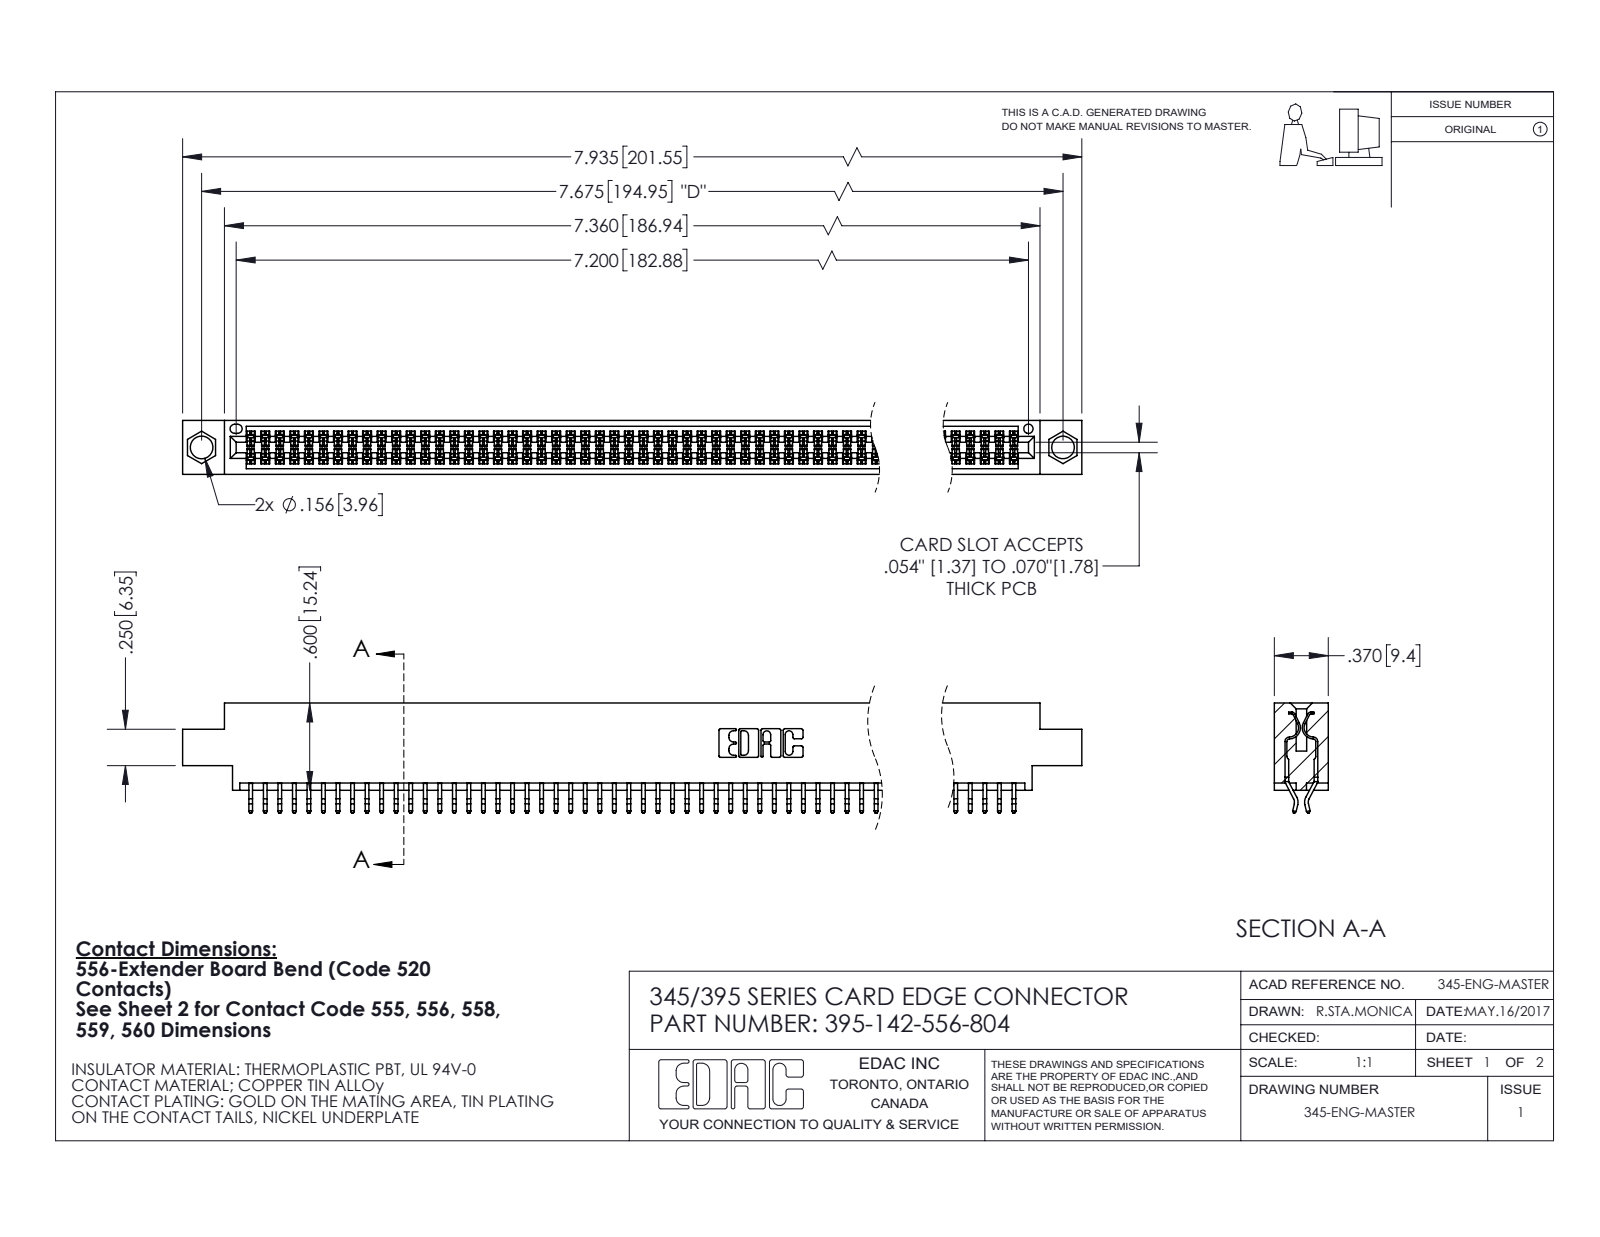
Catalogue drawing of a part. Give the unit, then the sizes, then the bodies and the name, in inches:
Units: inches
Overall size (bounding box): 7.935 × 0.757 × 0.37
Round holes (diameter × count): ⌀0.156 ×2, ⌀0.064 ×1
Partial cylindrical surfaces — rounded edges, fillets, slot ends (radius × count): R0.006 ×284, R0.01 ×22, R0.007 ×6, R0.031 ×6, R0.026 ×3, R0.01 ×2, R0.014 ×2, R0.019 ×2
Main face-to-face distances: 0.072, 0.298, 0.37, 0.2, 0.025, 0.098, 0.272, 0.225, 0.175, 0.149
Hole centre spacings: 0.27, 7.439, 7.675
Volume: 1.197 in³ · Surface area: 45.63 in²
Bodies: 143 solids, 8096 faces (5352 planar, 2744 cylindrical, 0 other)
Part name (STEP PRODUCT): 395-142-556-804; 345-292-001_556 Tail; 345 Part_0.170 Offset - 0.156 Dia-TI
STEP written by: SolidWorks 2020 (CONFIG_CONTROL_DESIGN)
